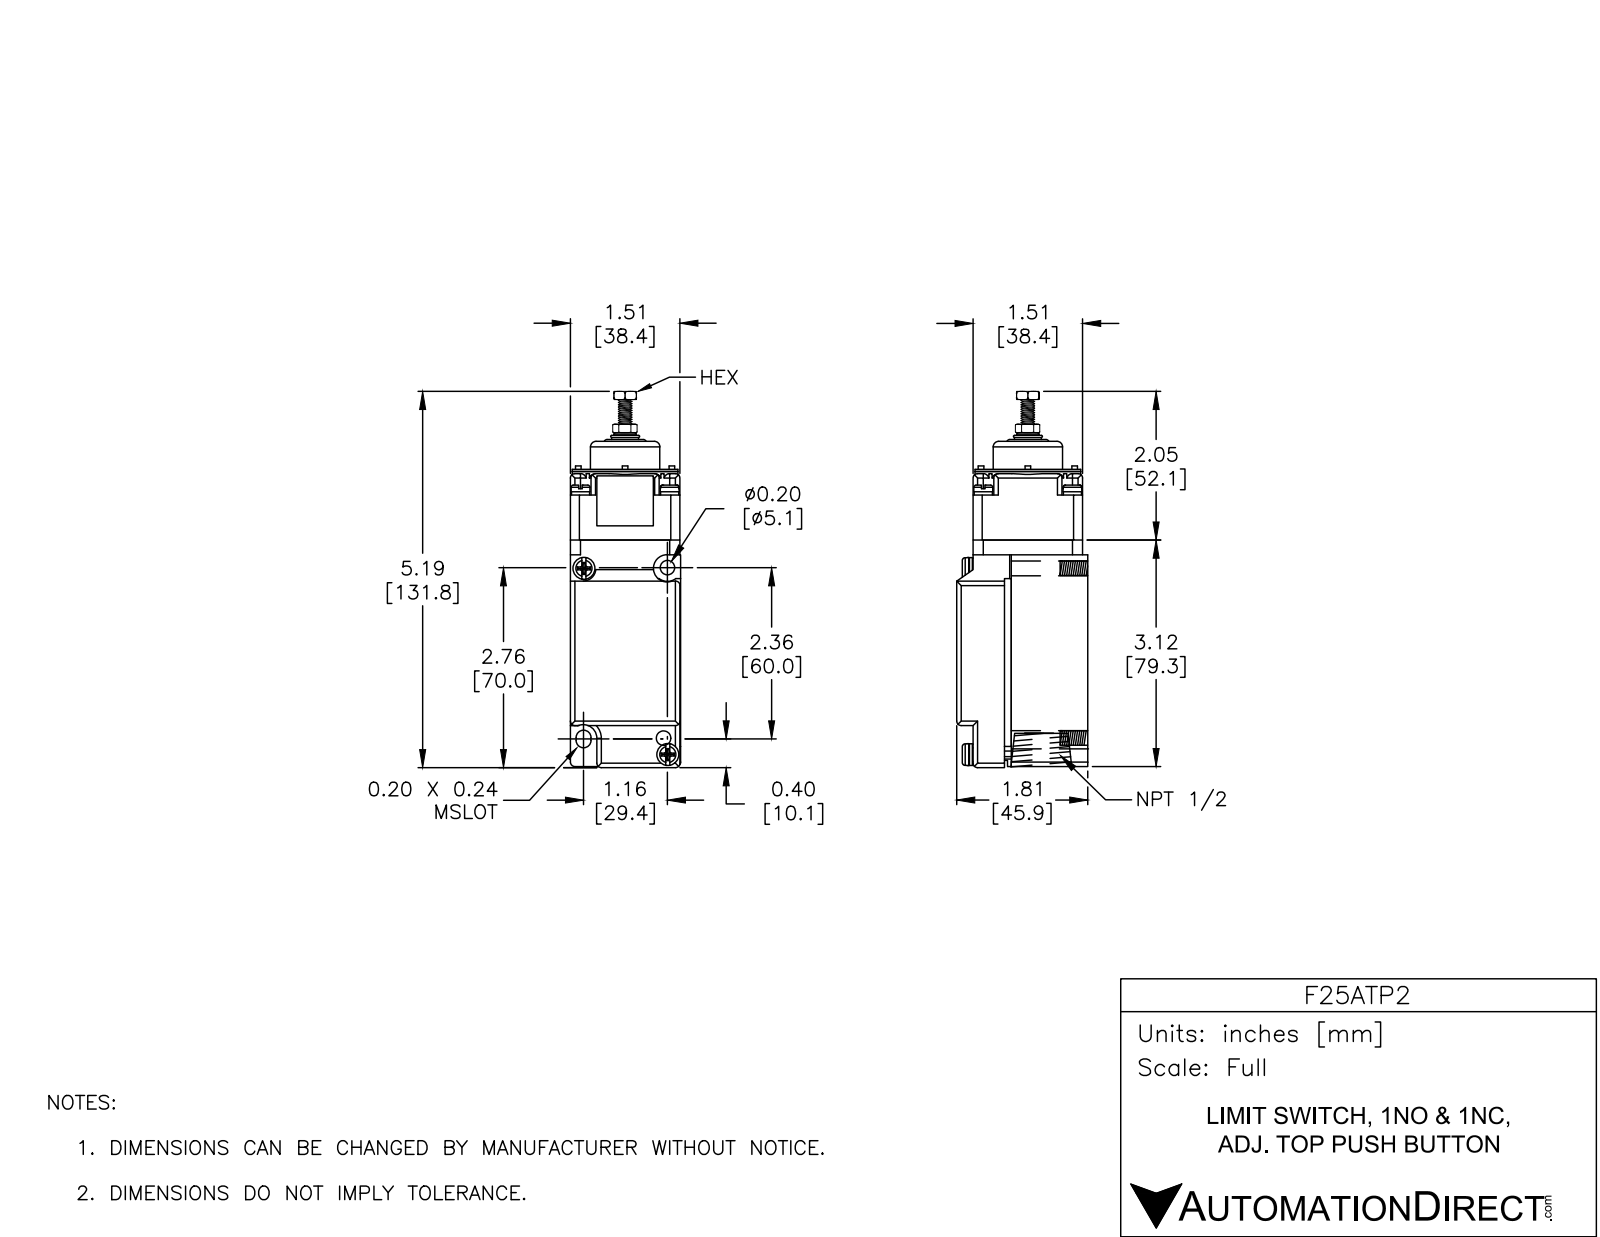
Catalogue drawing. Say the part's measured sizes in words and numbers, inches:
The part is named "F25ATP2". Its 3-D file was written by "SolidWorks 2018 (AUTOMOTIVE_DESIGN)". It is 17 solids with 863 faces: 272 planar, 142 cylindrical and 449 other. Overall it measures 5.189 by 1.809 by 1.52 inches. Its volume is 10.04 cubic inches and its surface area 80.96 square inches. Round holes: 4 of diameter 0.077, 4 of diameter 0.177, 3 of diameter 0.19, 3 of diameter 0.2, 1 of diameter 0.096, 1 of diameter 0.23, 1 of diameter 0.92, 1 of diameter 1.054. Round bosses or shafts: 5 of diameter 0.25, 4 of diameter 0.26, 4 of diameter 0.14, 2 of diameter 0.302, 2 of diameter 0.3, 1 of diameter 1.458, 1 of diameter 0.956, 1 of diameter 0.4. Partial cylindrical surfaces (rounded edges, fillets, slot ends): 21 of radius 0.062, 16 of radius 0.03, 8 of radius 0.015, 8 of radius 0.062, 4 of radius 0.14, 4 of radius 0.145, 2 of radius 0.102, 2 of radius 0.188. The main face-to-face distances are 0.094, 1.149, 1.055, 1.52, 0.945, 0.66, 0.754, 1.809, 1.51, 0.227. The hole center spacings are 1.403, 0.616, 0.646, 0.616, 0.87, 0.87, 0.913, 0.914.
